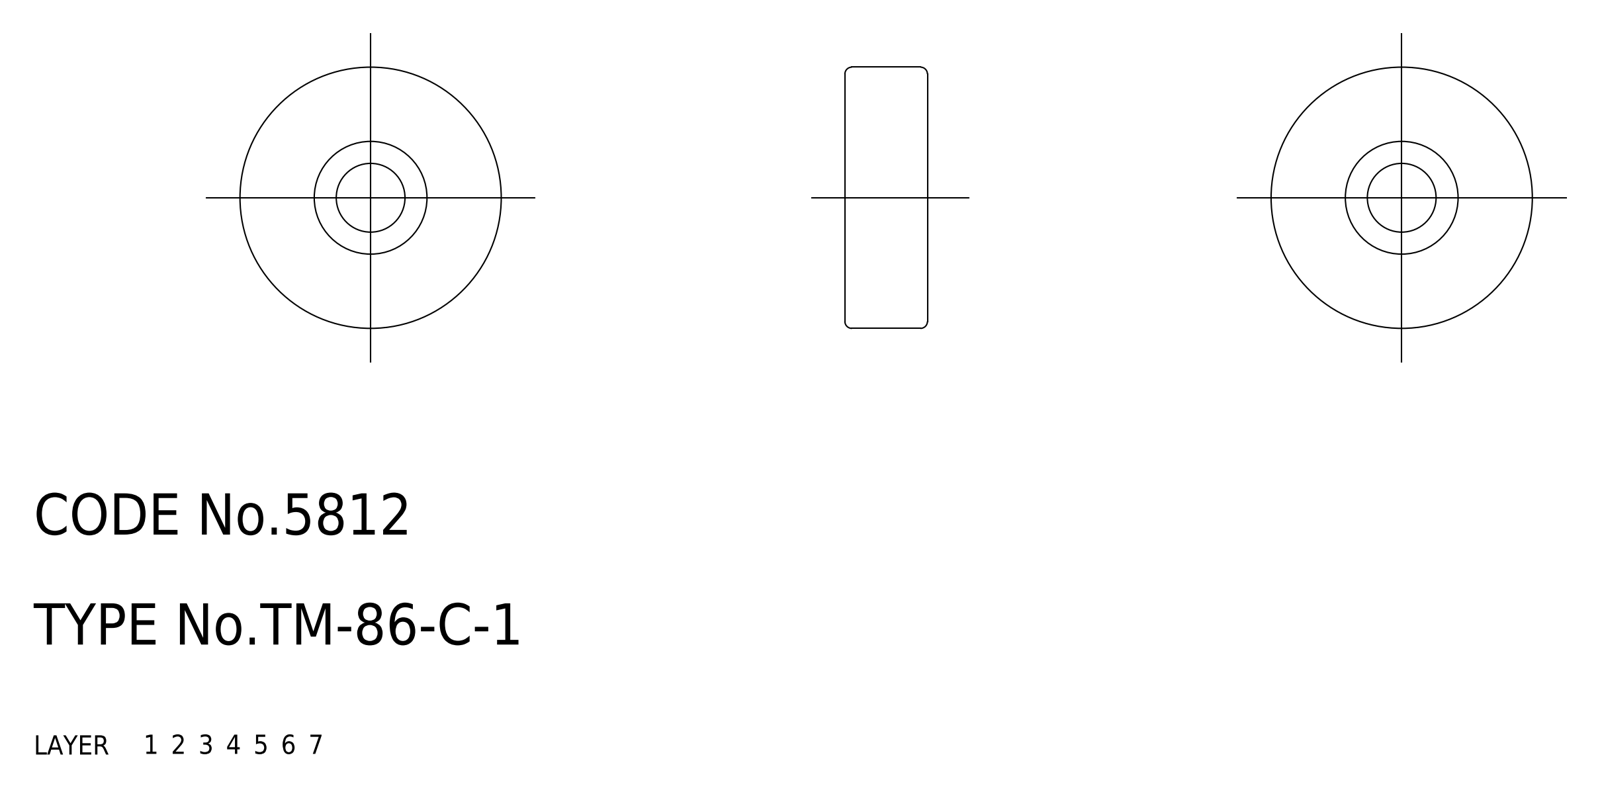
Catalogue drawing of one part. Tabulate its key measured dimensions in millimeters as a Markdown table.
| quantity | value |
| --- | --- |
| part name | roller |
| STEP written by | CADfix (AUTOMOTIVE_DESIGN) |
| units | millimeters |
| bodies | 1 solid, 28 faces (0 planar, 0 cylindrical, 28 other) |
| overall size | 19 × 19 × 6 |
| volume | 1 580 mm³ |
| surface area | 1 330 mm² |
